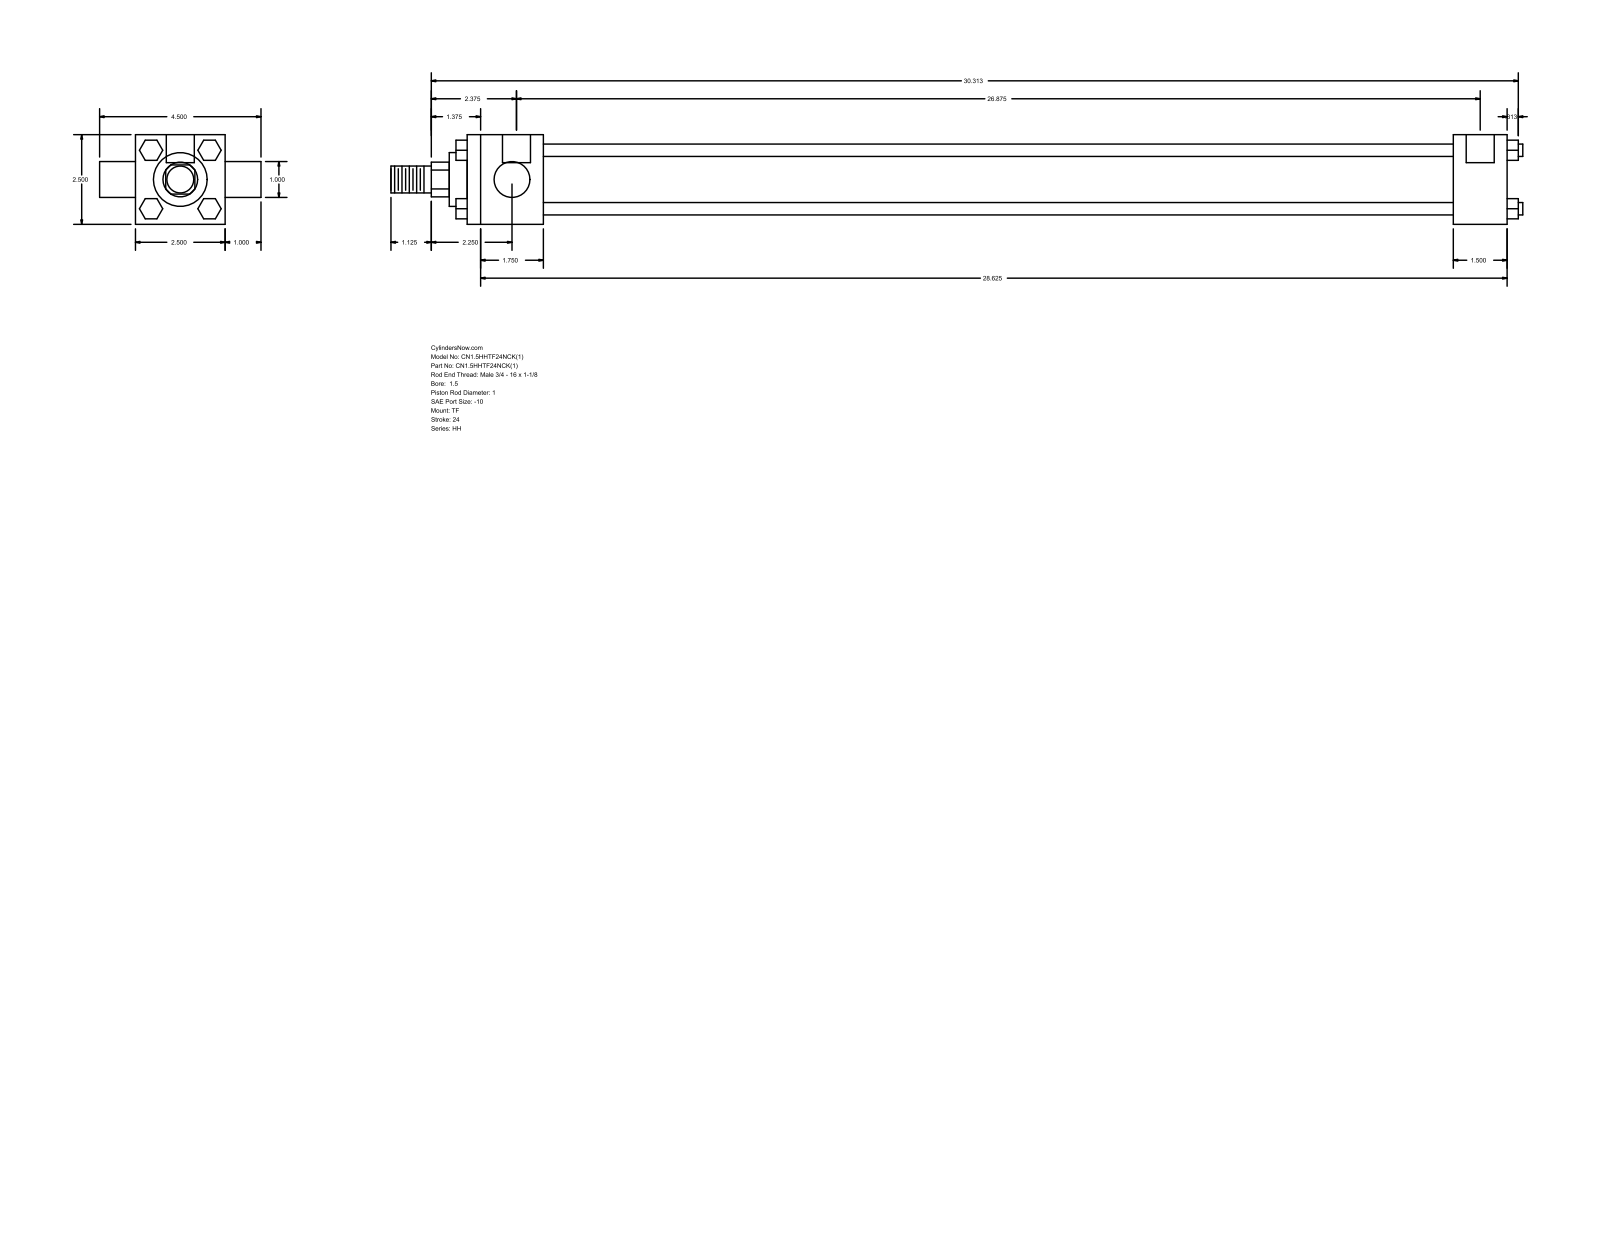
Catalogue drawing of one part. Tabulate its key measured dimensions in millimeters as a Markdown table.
| quantity | value |
| --- | --- |
| part name | HH_TF__0150_1 |
| STEP written by | GSSL Pune (CONFIG_CONTROL_DESIGN) |
| units | millimeters |
| bodies | 0 solids, 120 faces (92 planar, 28 cylindrical, 0 other) |
| overall size | 801.69 × 114.3 × 63.5 |
| round holes (diameter × count) | 5.56 × 3, 19.84 × 2 |
| round bosses / shafts (diameter × count) | 8.76 × 4, 25.4 × 2, 44.45 × 1, 38.1 × 1, 19.05 × 1 |
| partial cylindrical surfaces (radius × count) | 12.29 × 1 |
| main face-to-face distances | 63.5, 38.1, 682.62, 644.52, 53.98, 698.5, 736.6, 25.4, 20.7, 14.29 |
| hole center spacings | 1.59, 684.21, 682.62, 685.8 |
